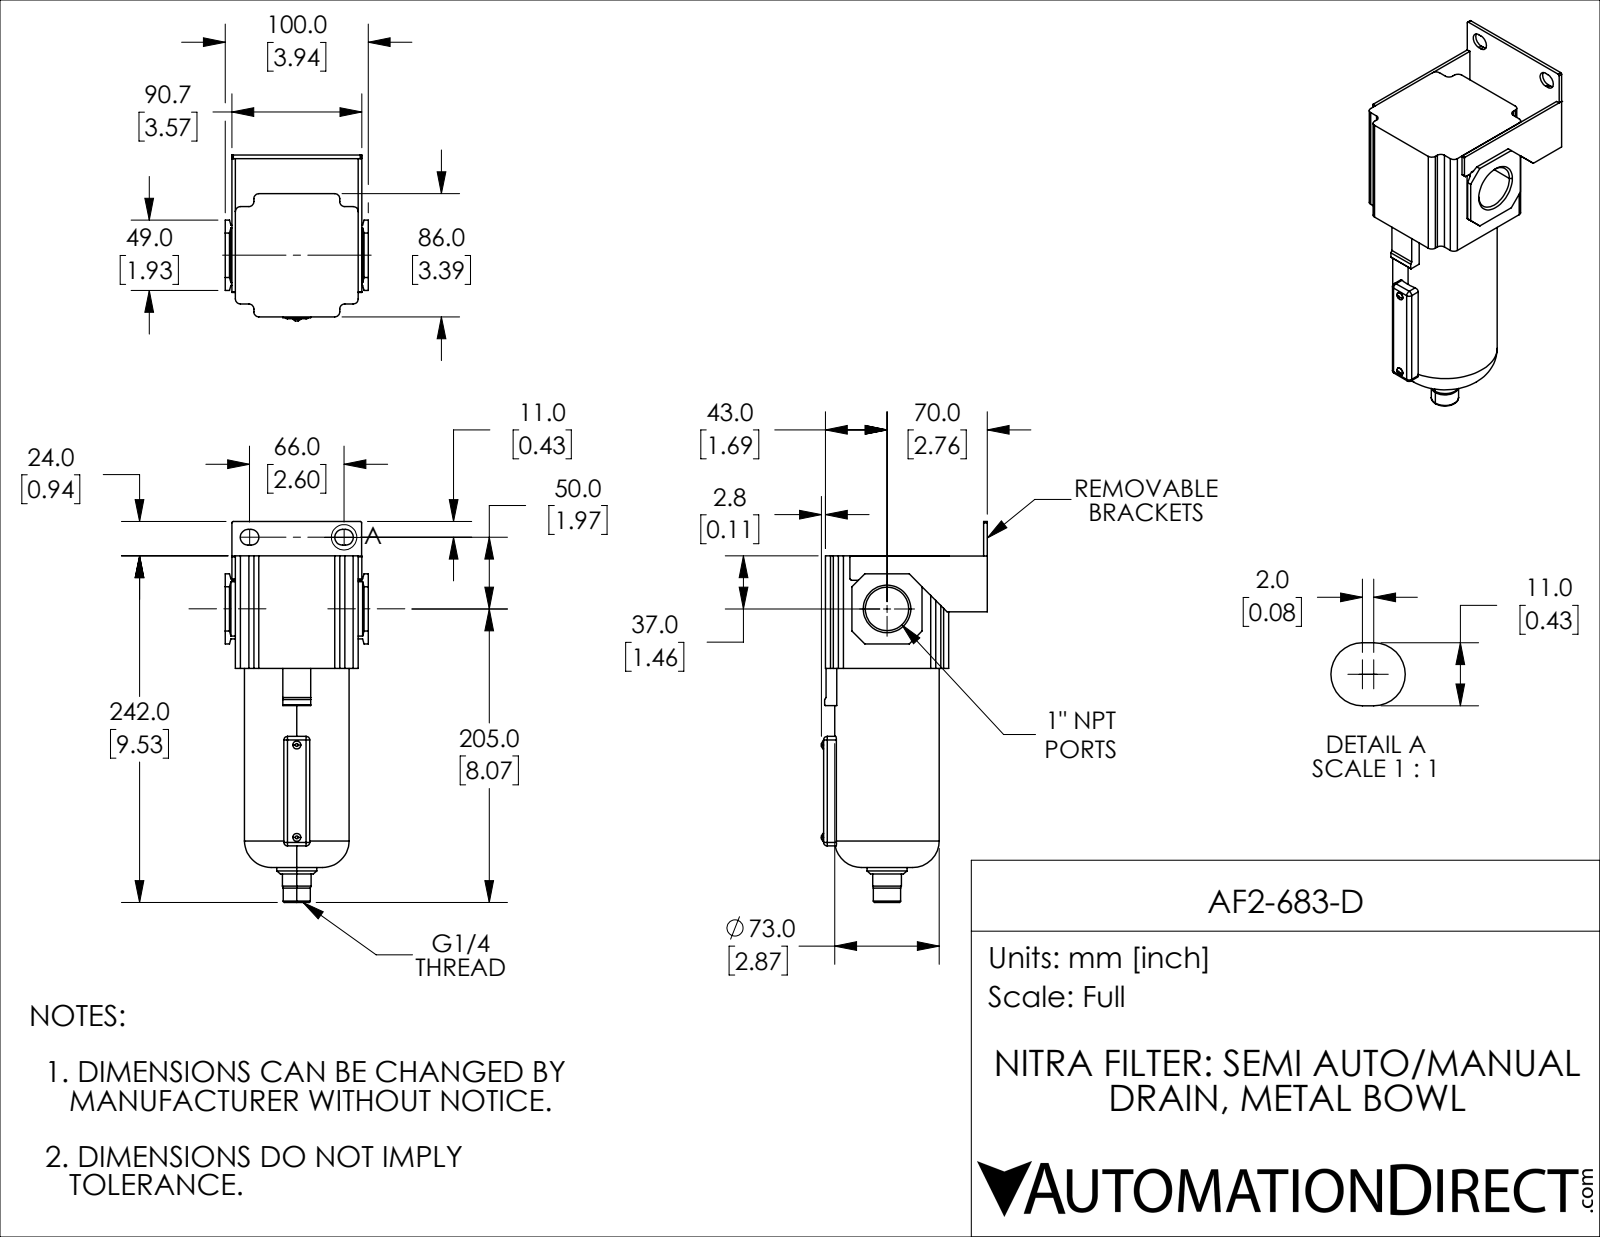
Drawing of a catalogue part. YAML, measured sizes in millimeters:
part_name: "AF2-683-D"
step_written_by: "SolidWorks 2019 (CONFIG_CONTROL_DESIGN)"
units: millimeters
bodies: {solids: 1, faces: 160, planar: 94, cylindrical: 44, other: 22}
overall_size: [266, 115.8, 100]
volume: 1137000
surface_area: 100847
round_holes:
  - {diameter: 8.57, count: 1}
  - {diameter: 30.29, count: 1}
round_bosses_or_shafts:
  - {diameter: 5.5, count: 2}
  - {diameter: 73, count: 1}
  - {diameter: 28, count: 1}
  - {diameter: 20, count: 1}
  - {diameter: 19, count: 1}
partial_cylinders:
  - {radius: 3.5, count: 12}
  - {radius: 2.5, count: 8}
  - {radius: 5.5, count: 4}
  - {radius: 1, count: 2}
face_to_face_distances: [2.5, 88.2, 24.5, 113, 86, 27, 110.5, 85.7, 4.65, 7.15]
